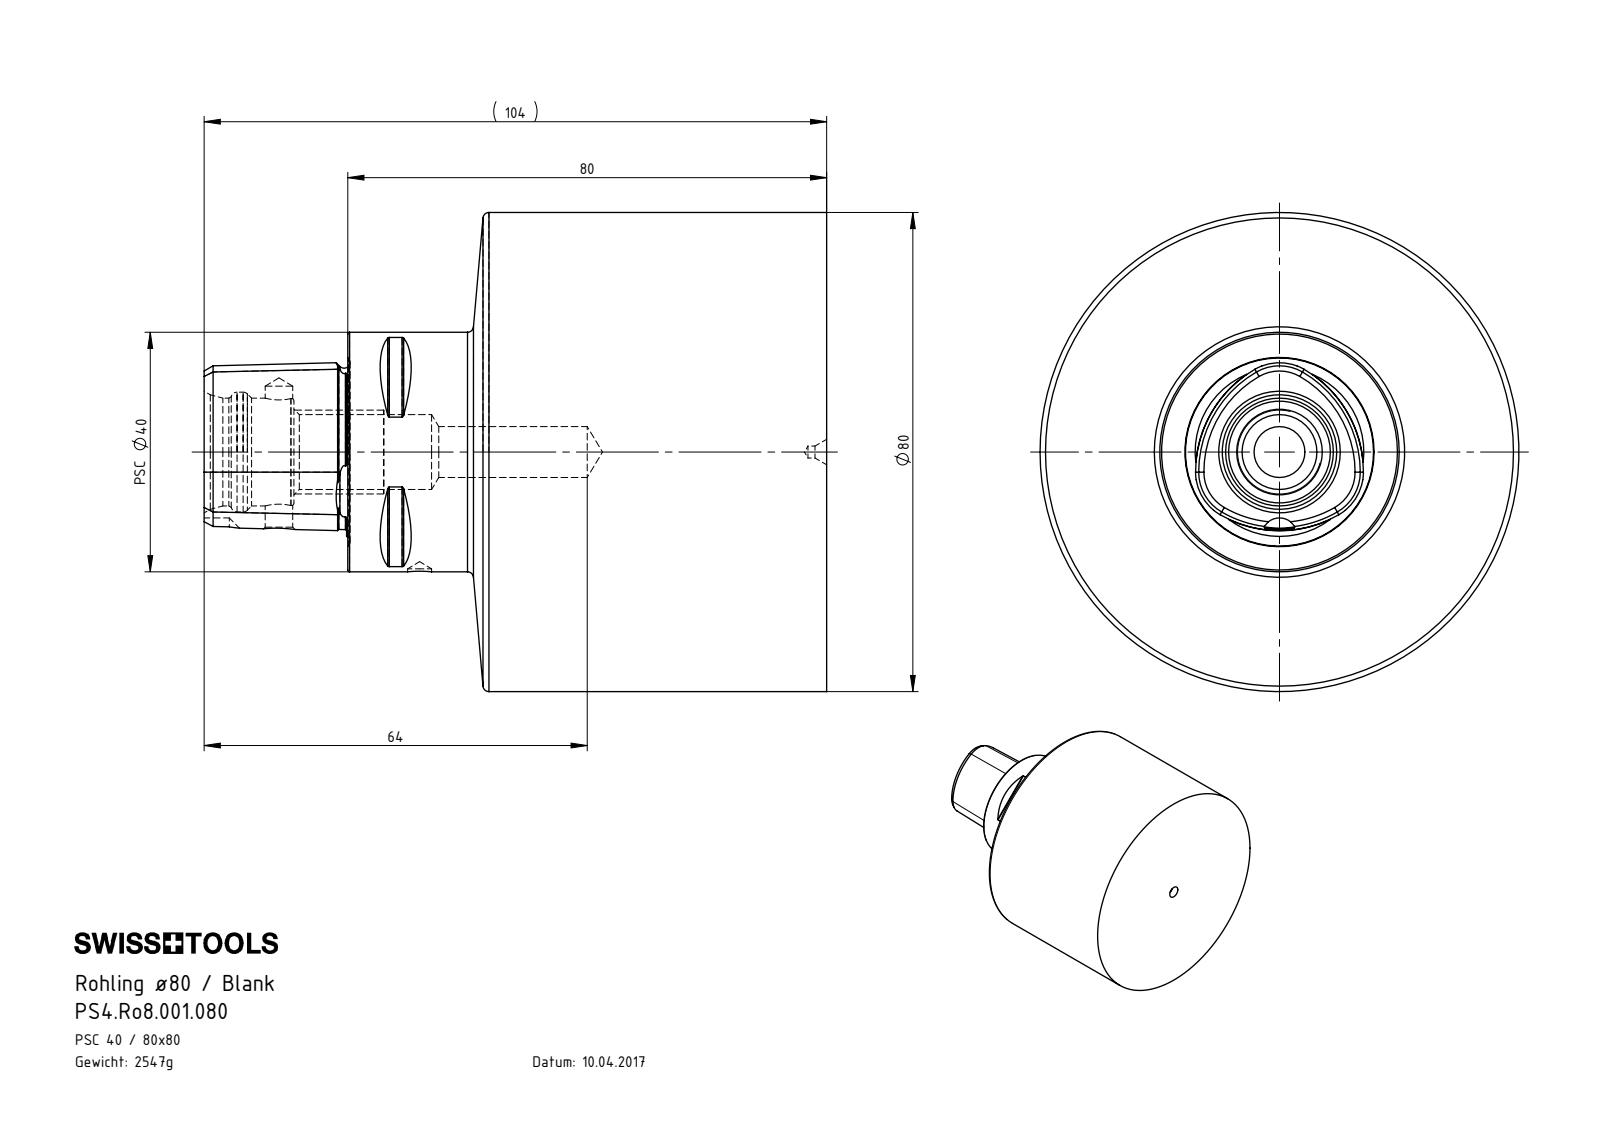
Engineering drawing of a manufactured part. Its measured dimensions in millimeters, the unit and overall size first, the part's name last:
Units: millimetres
Overall size (bounding box): 104 × 80 × 80
Round holes (diameter × count): ⌀2 ×1, ⌀4 ×1, ⌀4.6 ×1, ⌀8.5 ×1, ⌀12.5 ×1, ⌀18 ×1, ⌀20 ×1
Round bosses / shafts (diameter × count): ⌀80 ×1, ⌀40 ×1
Partial cylindrical surfaces — rounded edges, fillets, slot ends (radius × count): R0.3 ×8, R3 ×1
Main face-to-face distances: 80, 24, 104, 15.52, 35.3, 15, 9, 89, 23.8, 8.8
Hole centre spacings: 23.5
Volume: 324 420 mm³ · Surface area: 31 609 mm²
Bodies: 1 solid, 98 faces (19 planar, 20 cylindrical, 59 other)
Part name (STEP PRODUCT): PS4.Ro8.001.080
STEP written by: SolidWorks 2017 (AUTOMOTIVE_DESIGN)
